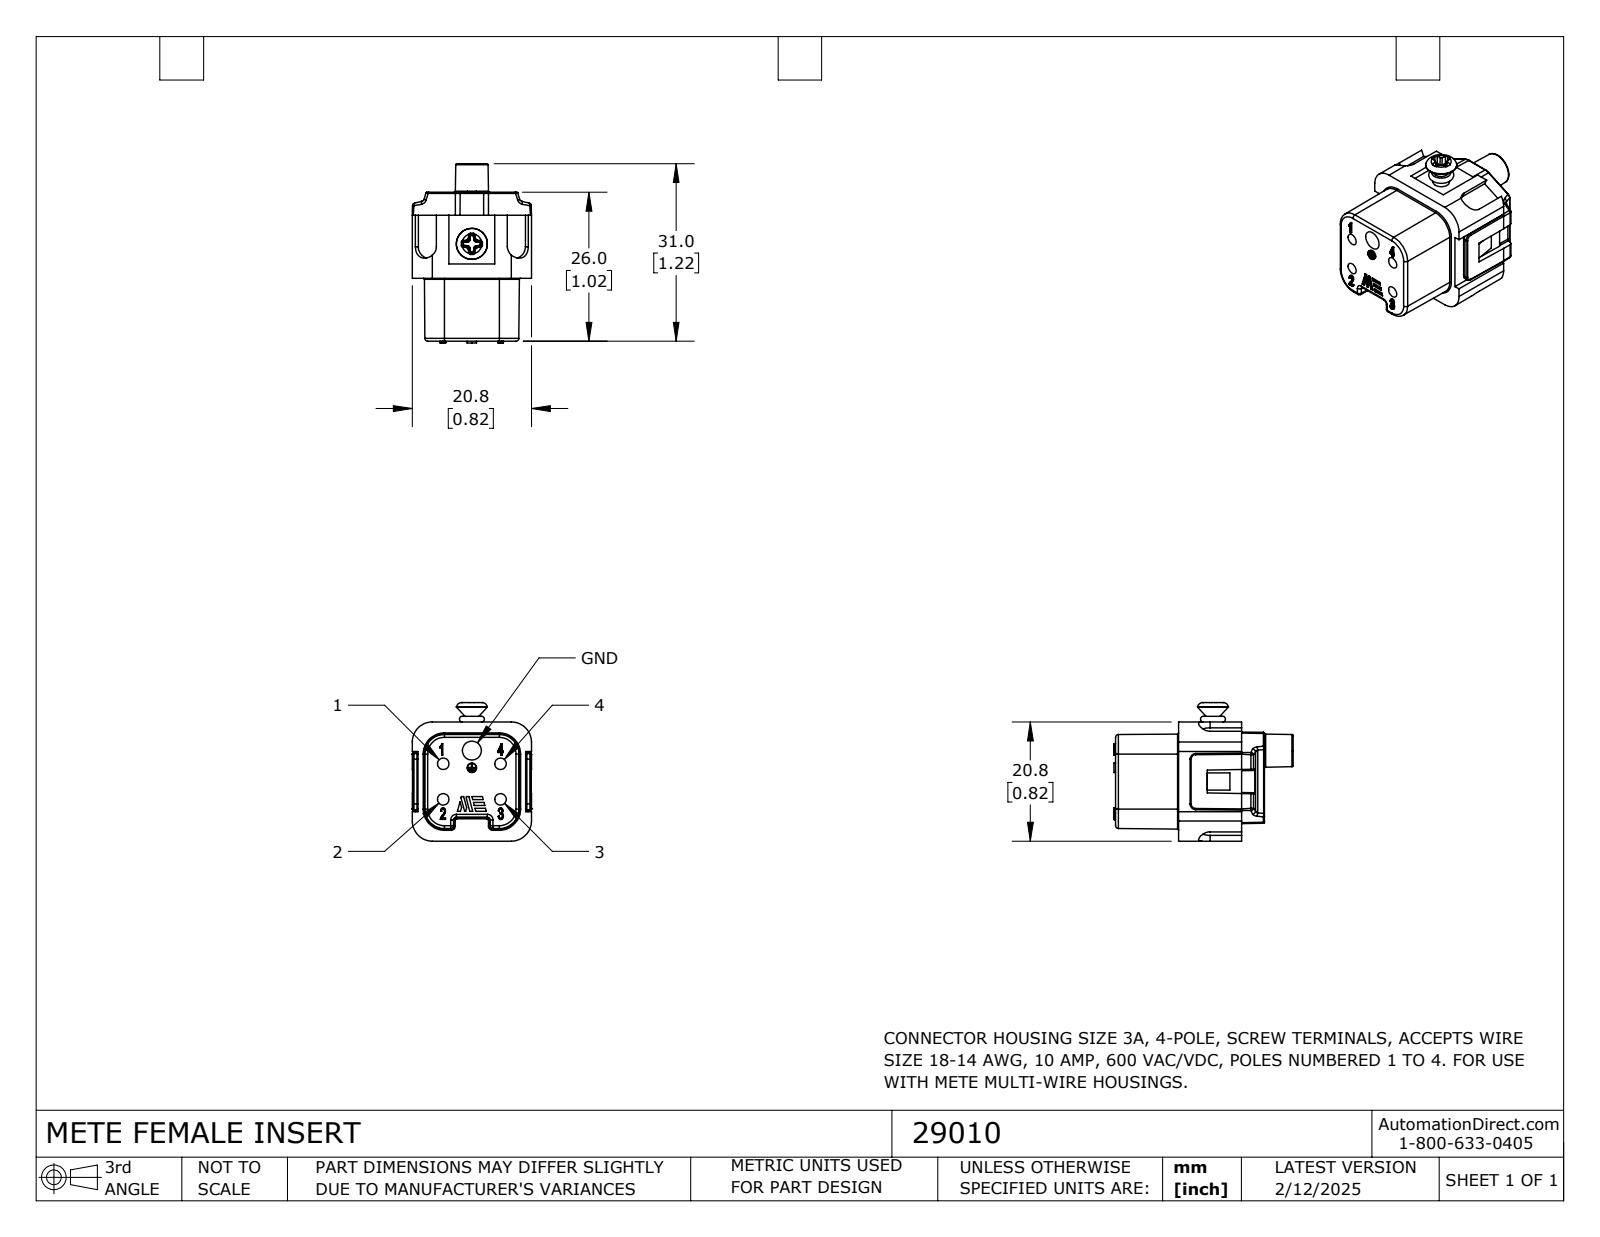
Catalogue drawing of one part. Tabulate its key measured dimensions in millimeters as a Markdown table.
| quantity | value |
| --- | --- |
| part name | 29010 |
| STEP written by | SolidWorks 2024 (CONFIG_CONTROL_DESIGN) |
| units | millimeters |
| bodies | 1 solid, 641 faces (266 planar, 193 cylindrical, 182 other) |
| overall size | 31.3 × 24.2 × 20.8 |
| volume | 7 728 mm³ |
| surface area | 4 055 mm² |
| round holes (diameter × count) | 2 × 4, 1.54 × 1, 2.87 × 1, 3.3 × 1 |
| round bosses / shafts (diameter × count) | 2.87 × 5, 2.35 × 5, 4.87 × 1, 1.65 × 1 |
| partial cylindrical surfaces (radius × count) | 0.2 × 37, 0.5 × 21, 0.1 × 12, 0.3 × 12, 2 × 9, 0.4 × 4, 3.5 × 4, 2.5 × 3 |
| main face-to-face distances | 11, 2, 22, 1, 4, 19.8, 15, 20.8, 26, 21.84 |
| hole center spacings | 5.05, 5.5, 6.2, 7.43, 9.86, 10, 11.77, 3 |
